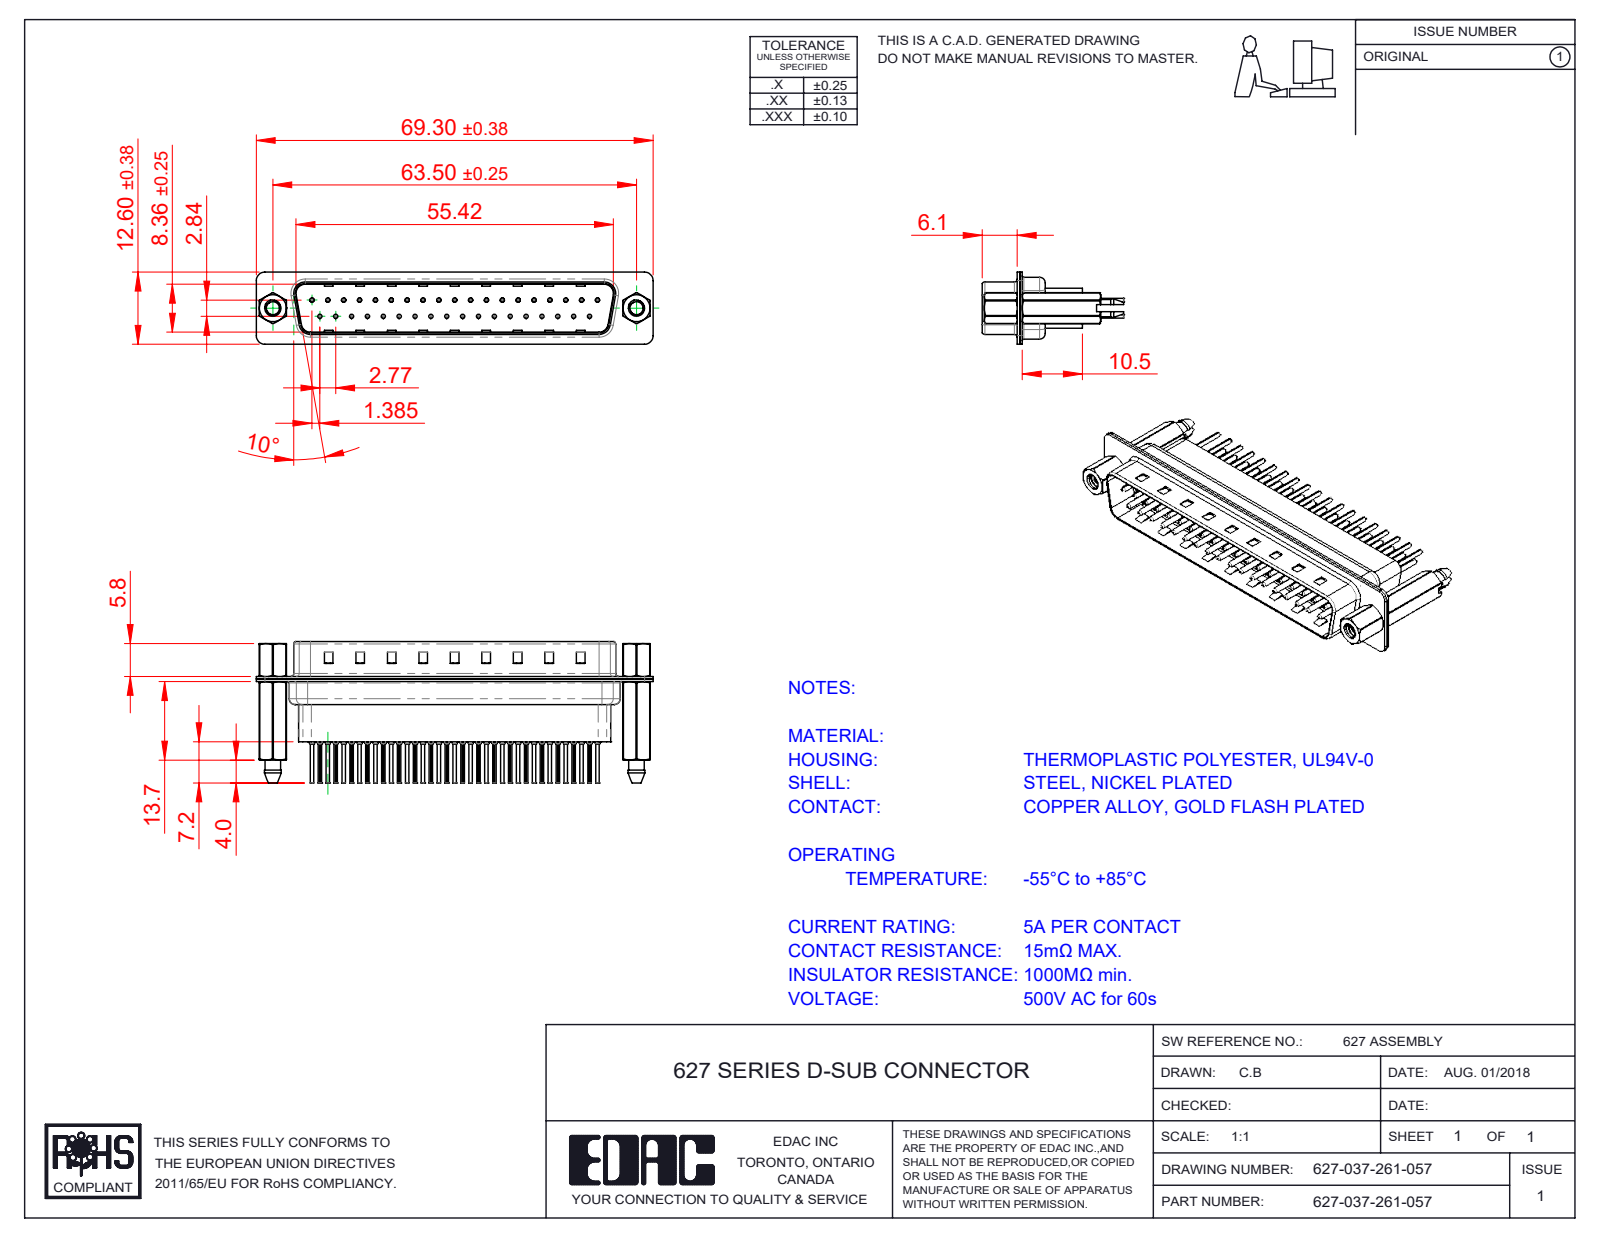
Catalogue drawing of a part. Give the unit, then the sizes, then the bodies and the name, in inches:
Units: inches
Overall size (bounding box): 2.728 × 0.969 × 0.496
Round holes (diameter × count): ⌀0.008 ×37, ⌀0.014 ×37, ⌀0.043 ×37, ⌀0.063 ×37, ⌀0.089 ×2, ⌀0.09 ×2, ⌀0.157 ×2, ⌀0.189 ×2
Round bosses / shafts (diameter × count): ⌀0.079 ×37, ⌀0.059 ×37, ⌀0.03 ×37, ⌀0.024 ×37, ⌀0.193 ×2, ⌀0.11 ×2
Partial cylindrical surfaces — rounded edges, fillets, slot ends (radius × count): R0.004 ×74, R0.059 ×18, R0.079 ×12, R0.063 ×10, R0.02 ×8, R0.01 ×4, R0.024 ×4, R0.026 ×4
Main face-to-face distances: 0.016, 0.032, 0.377, 0.018, 0.027, 0.302, 0.059, 0.043, 0.318, 0.345
Hole centre spacings: 0.124, 0.109, 0.218, 0.327, 0.198, 0.398, 0.436, 0.503
Volume: 0.36 in³ · Surface area: 23.51 in²
Bodies: 44 solids, 4272 faces (1145 planar, 1648 cylindrical, 1479 other)
Part name (STEP PRODUCT): 627 4-40 Hex Standoff; 627 Contact Row 2_61; 627 4-40 Threaded Boardlock_HP61; 627-037-261-057 (+4 more)
STEP written by: SolidWorks 2020 (CONFIG_CONTROL_DESIGN)
